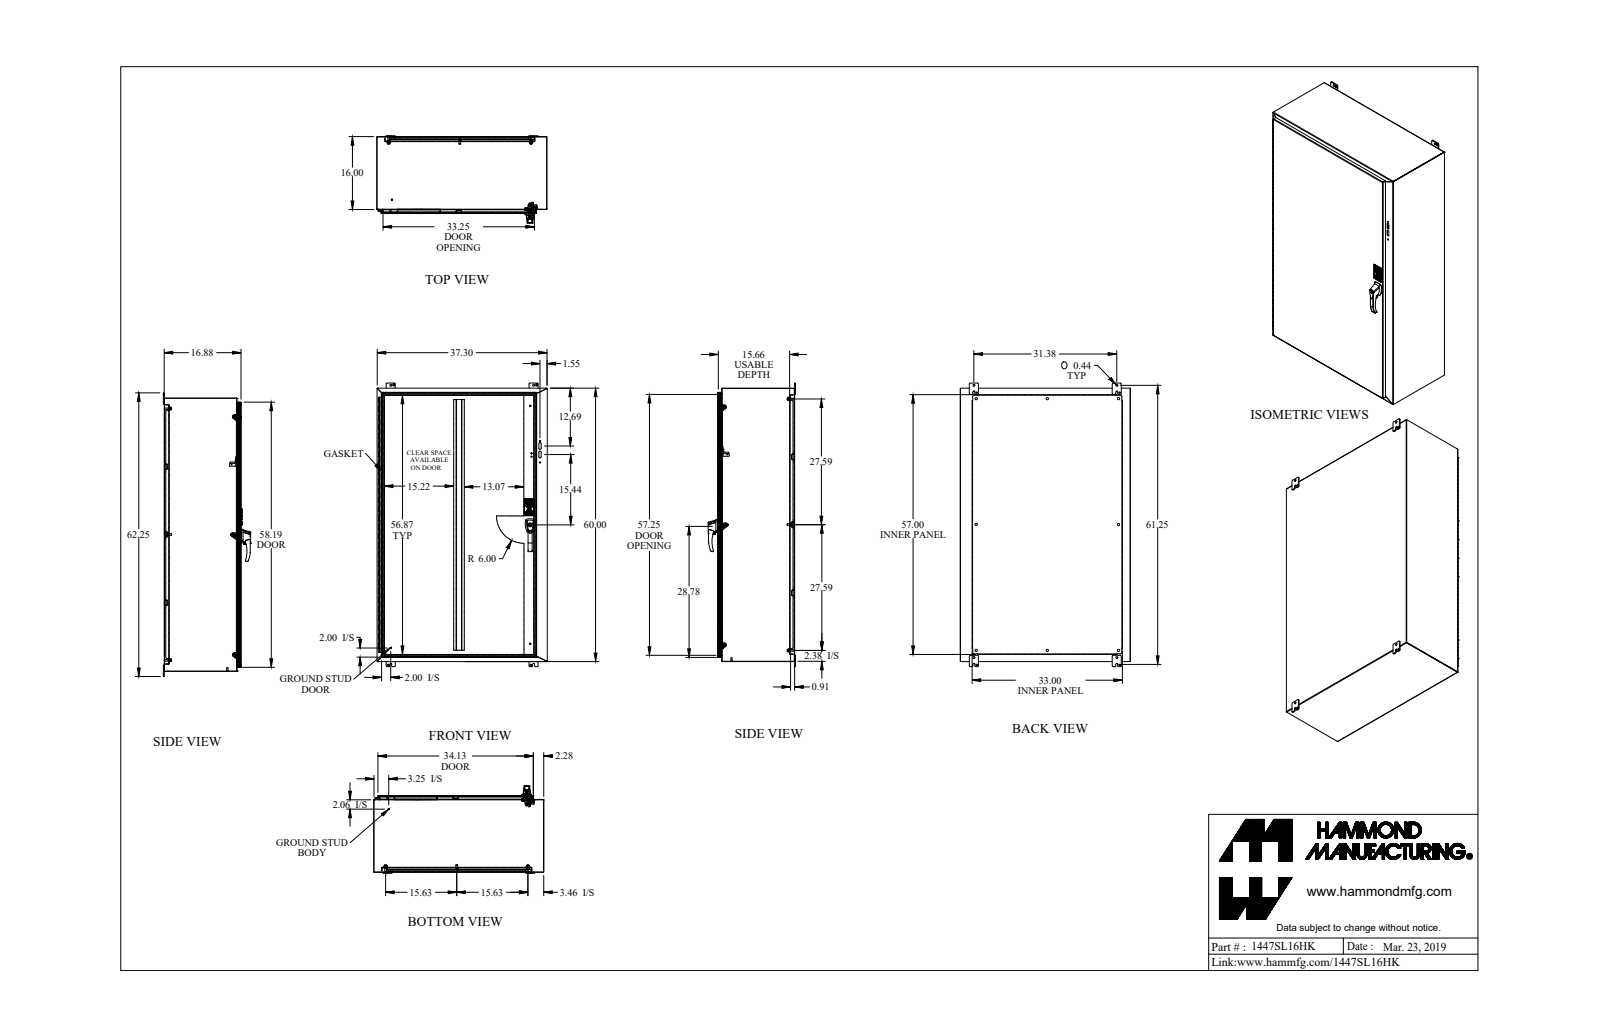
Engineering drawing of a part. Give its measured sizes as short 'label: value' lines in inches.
name: 1447SL16HK_Default
written by: SolidWorks 2019 (CONFIG_CONTROL_DESIGN)
unit: in
bodies: 71 solids, 2172 faces (1084 planar, 886 cylindrical, 202 other)
size: 62.25 × 37.375 × 19.177
volume: 843 in³; area: 21 787 in²
holes: 8× ⌀0.5, 6× ⌀0.176, 6× ⌀0.313, 4× ⌀0.307, 4× ⌀0.437, 4× ⌀0.445, 3× ⌀0.25, 3× ⌀0.265, 3× ⌀0.413, 2× ⌀0.156, 2× ⌀0.173, 2× ⌀0.196
bosses: 13× ⌀0.375, 9× ⌀0.25, 8× ⌀0.65, 8× ⌀0.33, 7× ⌀1, 6× ⌀0.156, 2× ⌀0.63, 2× ⌀0.51
rounds: 33× R0.188, 33× R0.25, 18× R0.036, 18× R0.108, 16× R0.116, 16× R0.125, 10× R0.03, 8× R0.218
face distances: 0.072, 16.803, 16.731, 16.875, 0.095, 37.303, 15.771, 15.699, 1.032, 1.104
hole spacings: 31.375, 57.417, 1.11, 31.25, 31.738, 55.25, 1.735, 1.736
